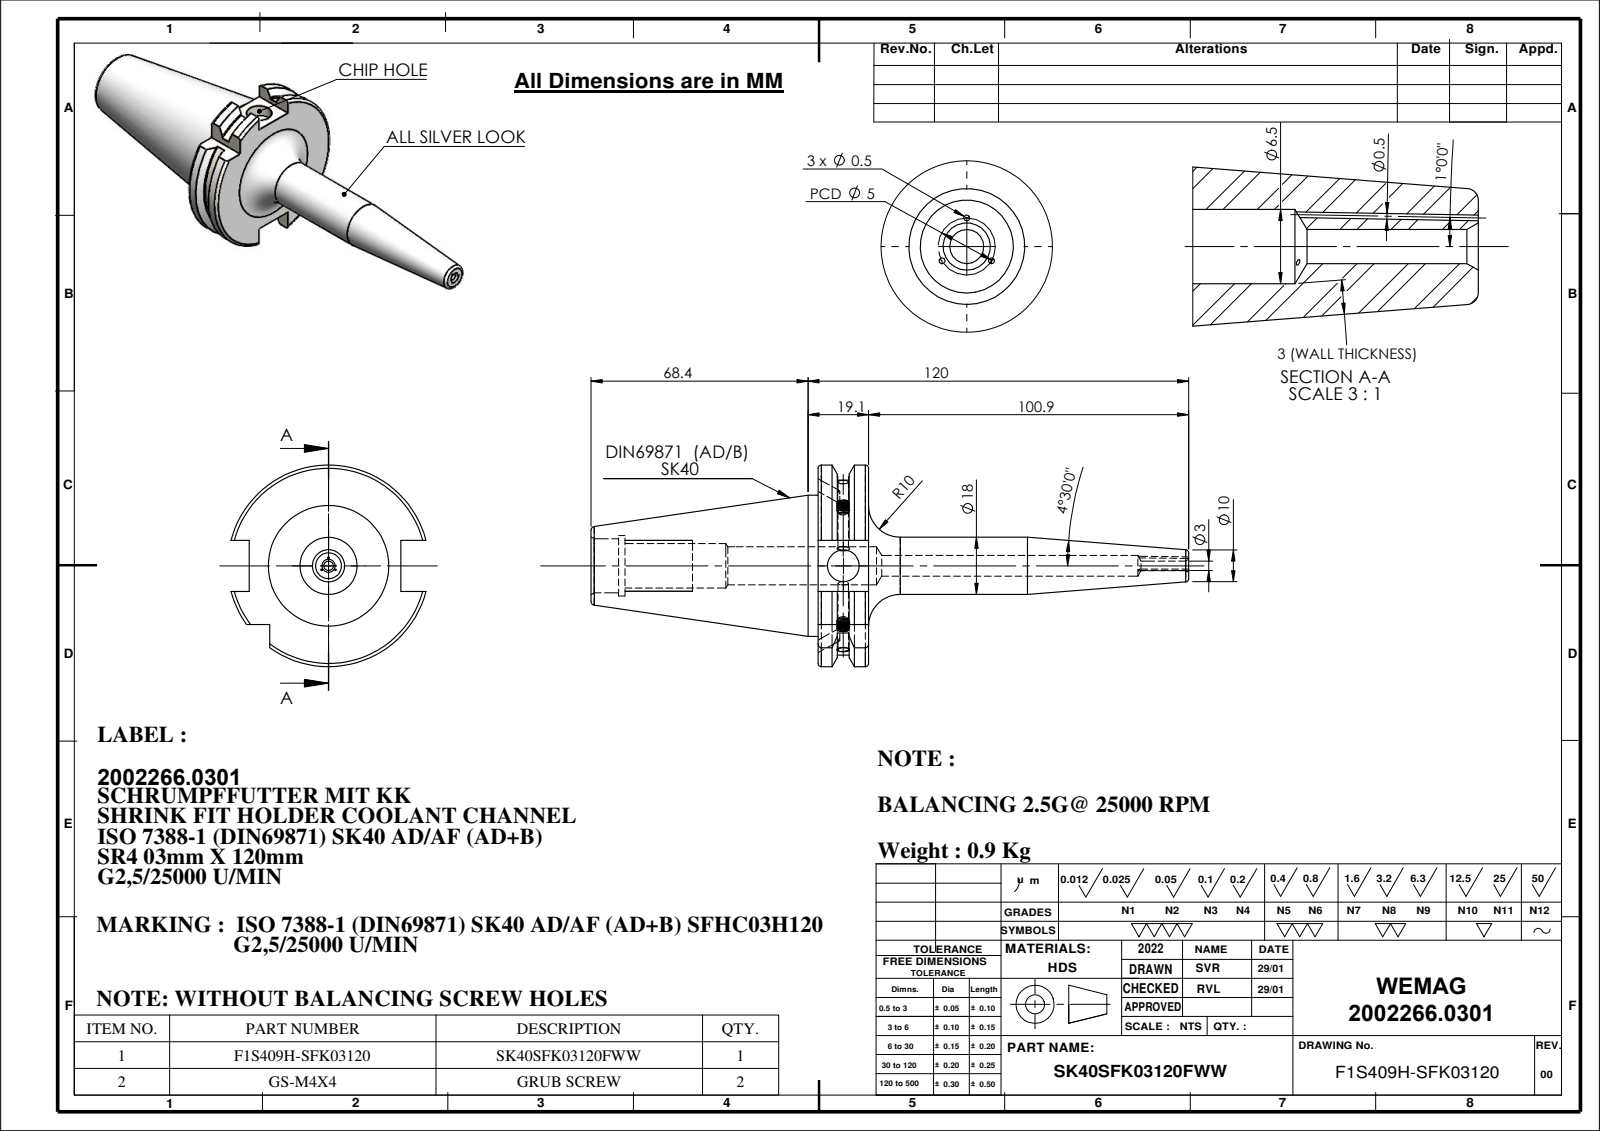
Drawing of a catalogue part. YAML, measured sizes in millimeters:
part_name: "SK40SFK03120FWW; 91406-SR403120; GS-M4X4_DIN 913 - M4 x 4-N"
step_written_by: "SolidWorks 2018 (CONFIG_CONTROL_DESIGN)"
units: millimeters
bodies: {solids: 3, faces: 202, planar: 46, cylindrical: 60, other: 96}
overall_size: [188.4, 63.55, 61.48]
volume: 119257
surface_area: 28131
round_holes:
  - {diameter: 0.5, count: 3}
  - {diameter: 2.99, count: 1}
  - {diameter: 3.3, count: 1}
  - {diameter: 6.5, count: 1}
  - {diameter: 10, count: 1}
  - {diameter: 12, count: 1}
  - {diameter: 14, count: 1}
  - {diameter: 17, count: 1}
  - {diameter: 19, count: 1}
round_bosses_or_shafts:
  - {diameter: 4, count: 2}
  - {diameter: 44.45, count: 1}
  - {diameter: 18, count: 1}
partial_cylinders:
  - {radius: 28.12, count: 1}
  - {radius: 31.77, count: 1}
face_to_face_distances: [15.9, 16.1, 47.8, 71.6, 87.5, 10.7, 60.9, 76.8, 77.63, 66.93]
